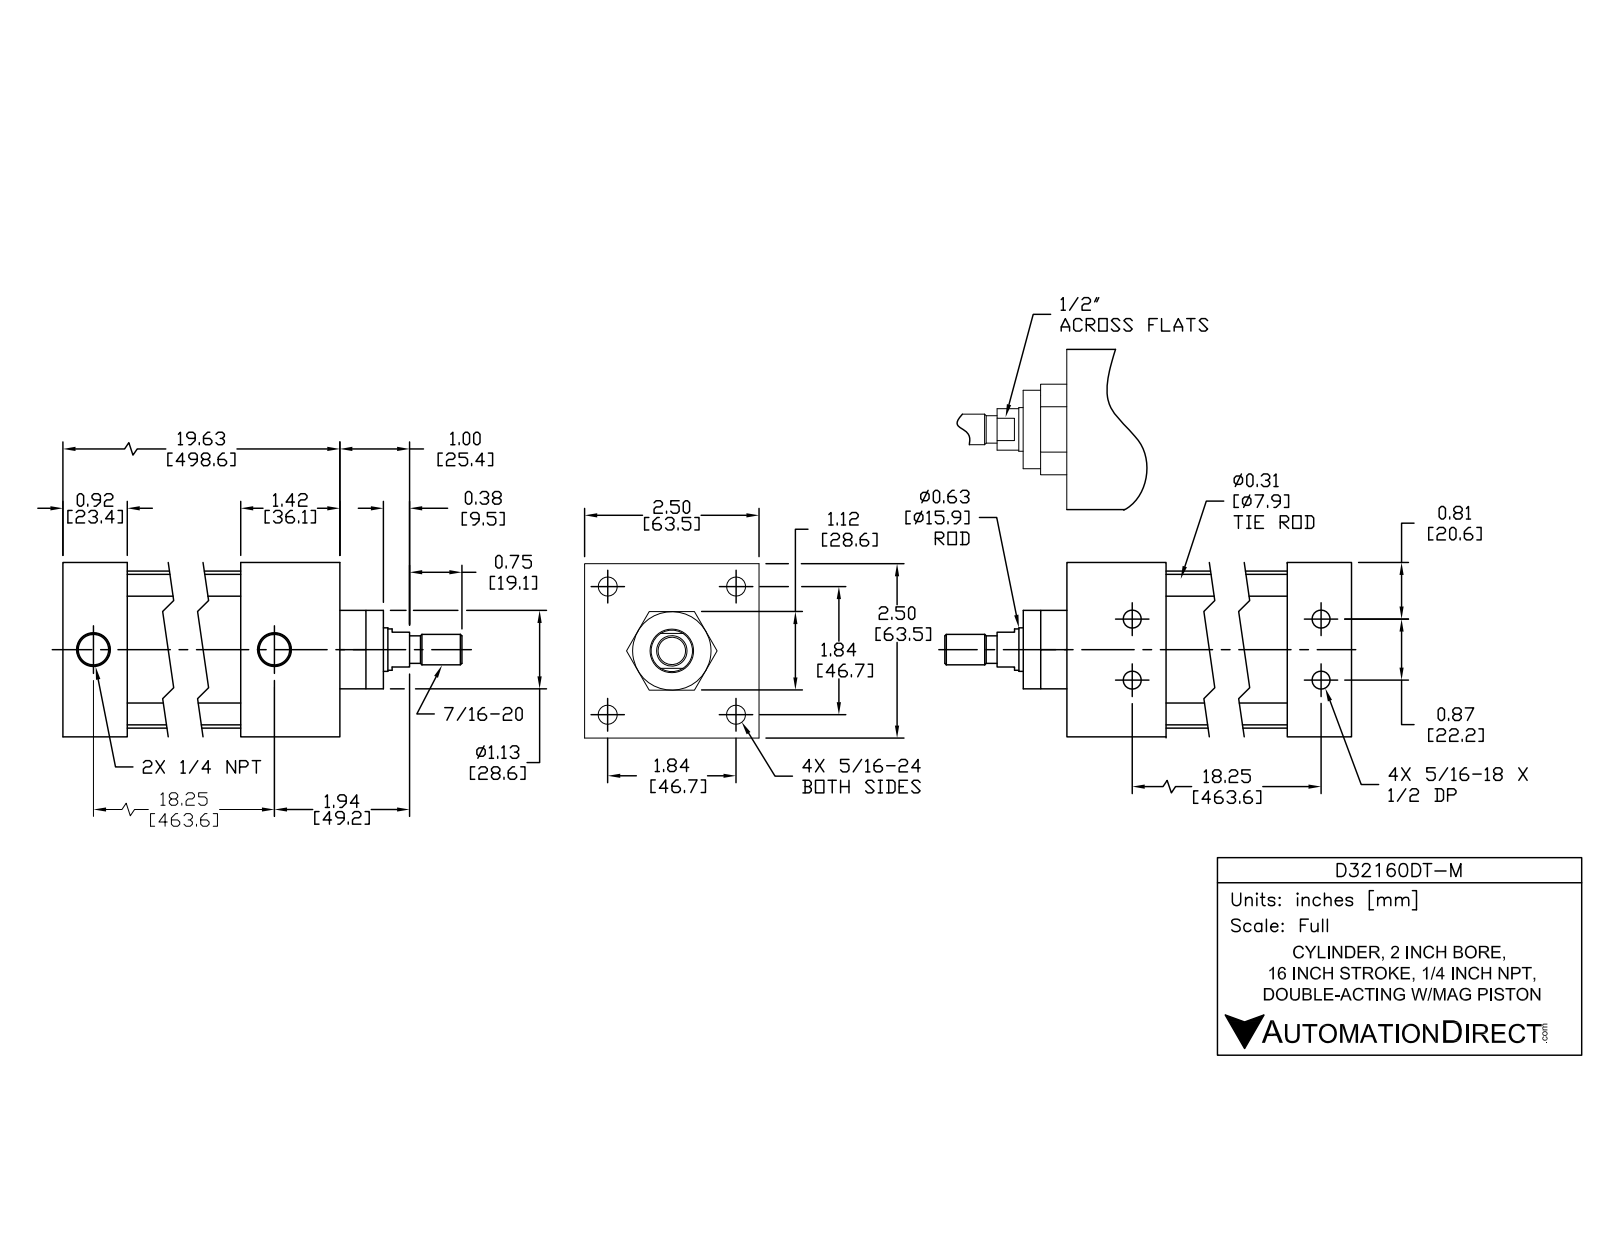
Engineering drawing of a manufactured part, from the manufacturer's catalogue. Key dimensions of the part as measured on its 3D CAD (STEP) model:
Part name (STEP PRODUCT): D32160DT-M BODY; D32160DT-M; D32160DT-M PISTON
STEP written by: SolidWorks 2015 (AUTOMOTIVE_DESIGN)
Units: inches
Bodies: 12 solids, 298 faces (94 planar, 114 cylindrical, 90 other)
Overall size (bounding box): 21.371 × 2.5 × 2.5
Volume: 42.05 in³ · Surface area: 425.1 in²
Round holes (diameter × count): ⌀0.252 ×4, ⌀0.267 ×4, ⌀0.359 ×4, ⌀0.5 ×4, ⌀0.297 ×2, ⌀0.477 ×2, ⌀0.625 ×1, ⌀0.628 ×1, ⌀2 ×1
Round bosses / shafts (diameter × count): ⌀0.484 ×4, ⌀0.313 ×4, ⌀0.282 ×4, ⌀2.25 ×1, ⌀1.997 ×1, ⌀1.12 ×1, ⌀0.622 ×1, ⌀0.59 ×1
Partial cylindrical surfaces — rounded edges, fillets, slot ends (radius × count): R0.25 ×4
Main face-to-face distances: 2.5, 19.621, 1.42, 18.201, 17.281, 18.701, 0.92, 1, 18.601, 17.181
Hole centre spacings: 0.437, 1.307, 1.848, 18.25, 18.245, 0.875, 2.613, 18.266
